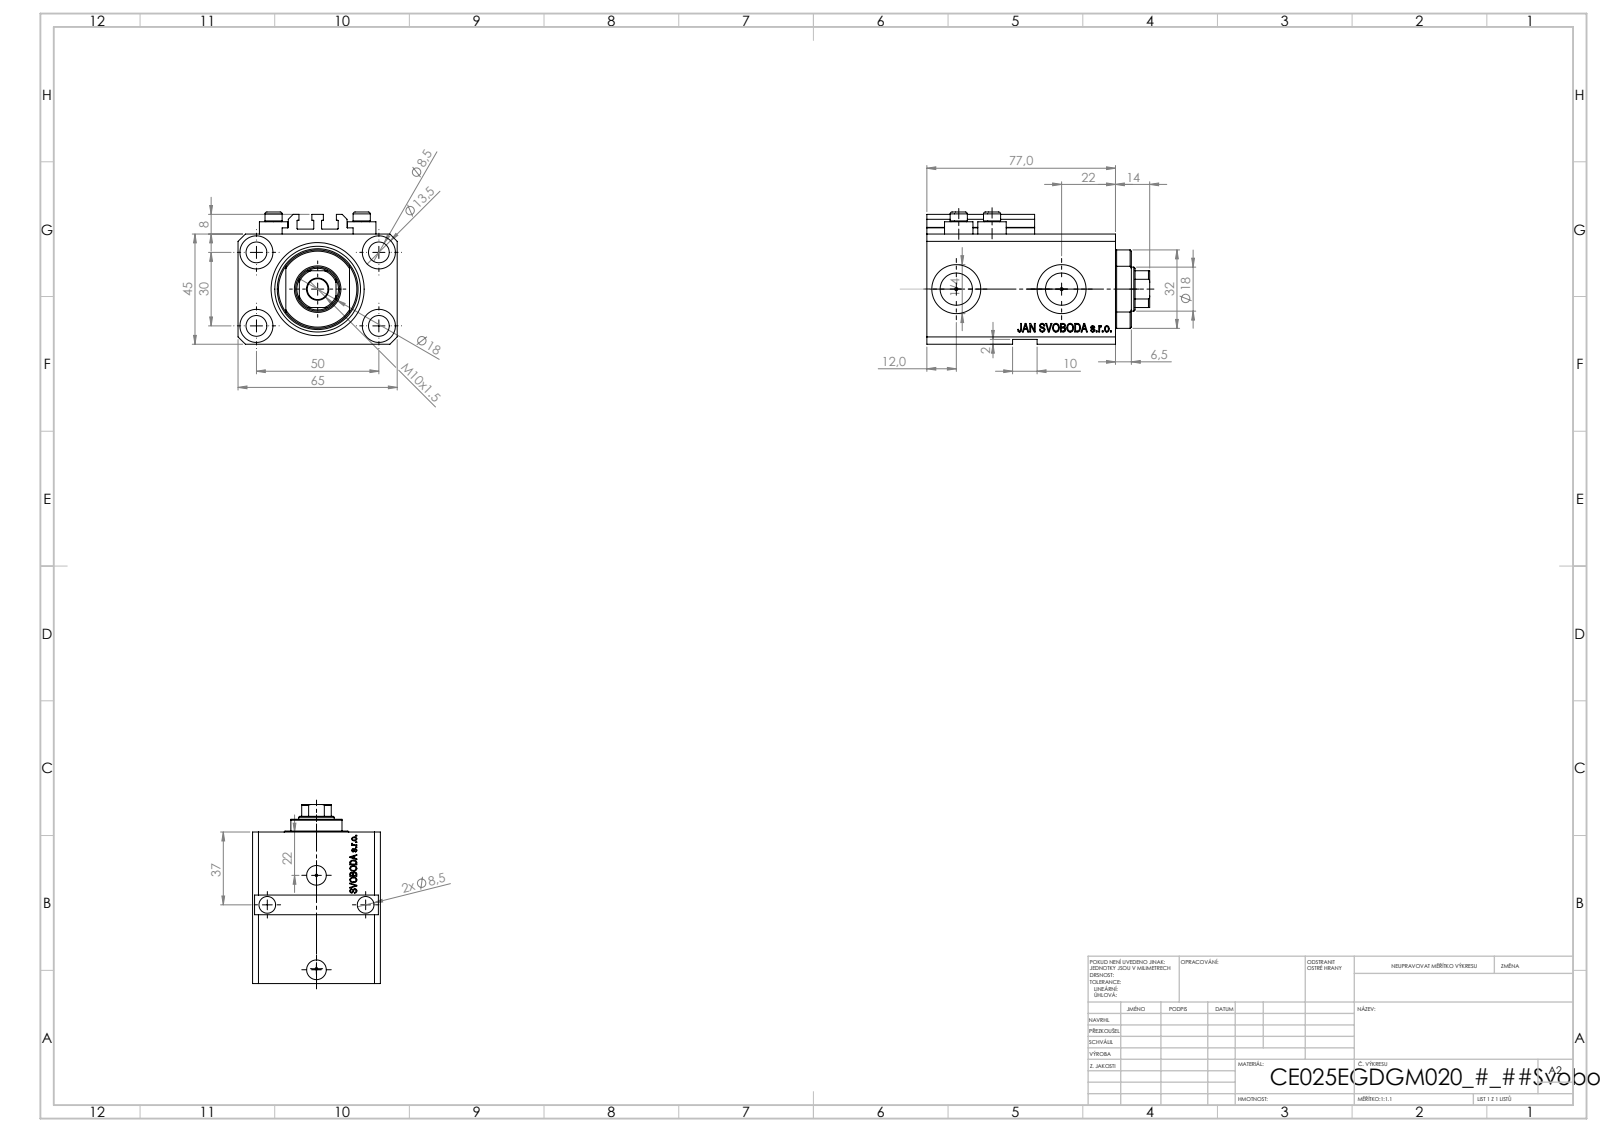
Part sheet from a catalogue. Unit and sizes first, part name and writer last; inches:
Units: inches
Overall size (bounding box): 3.583 × 2.559 × 2.126
Round holes (diameter × count): ⌀0.335 ×7, ⌀0.049 ×4, ⌀0.157 ×4, ⌀0.531 ×4, ⌀0.394 ×2, ⌀0.518 ×2, ⌀0.787 ×2, ⌀0.709 ×1, ⌀0.984 ×1, ⌀1.496 ×1
Round bosses / shafts (diameter × count): ⌀0.457 ×4, ⌀0.276 ×4
Partial cylindrical surfaces — rounded edges, fillets, slot ends (radius × count): R0.008 ×10, R0.335 ×1, R0.63 ×1
Main face-to-face distances: 1.772, 2.559, 2.48, 0.551, 3.031, 0.079, 0.272, 2.209, 2.76, 1.85
Hole centre spacings: 1.148, 1.969, 0.535, 0.595, 0.741, 0.747, 1.032, 1.048
Volume: 11.97 in³ · Surface area: 93.5 in²
Bodies: 8 solids, 1083 faces (515 planar, 138 cylindrical, 430 other)
Part name (STEP PRODUCT): V250CE_E_Body; ALLEN BOLT V250CE; V250CE_VC_E; V250CE_C_VCP
STEP written by: SolidWorks 2019 (CONFIG_CONTROL_DESIGN)
